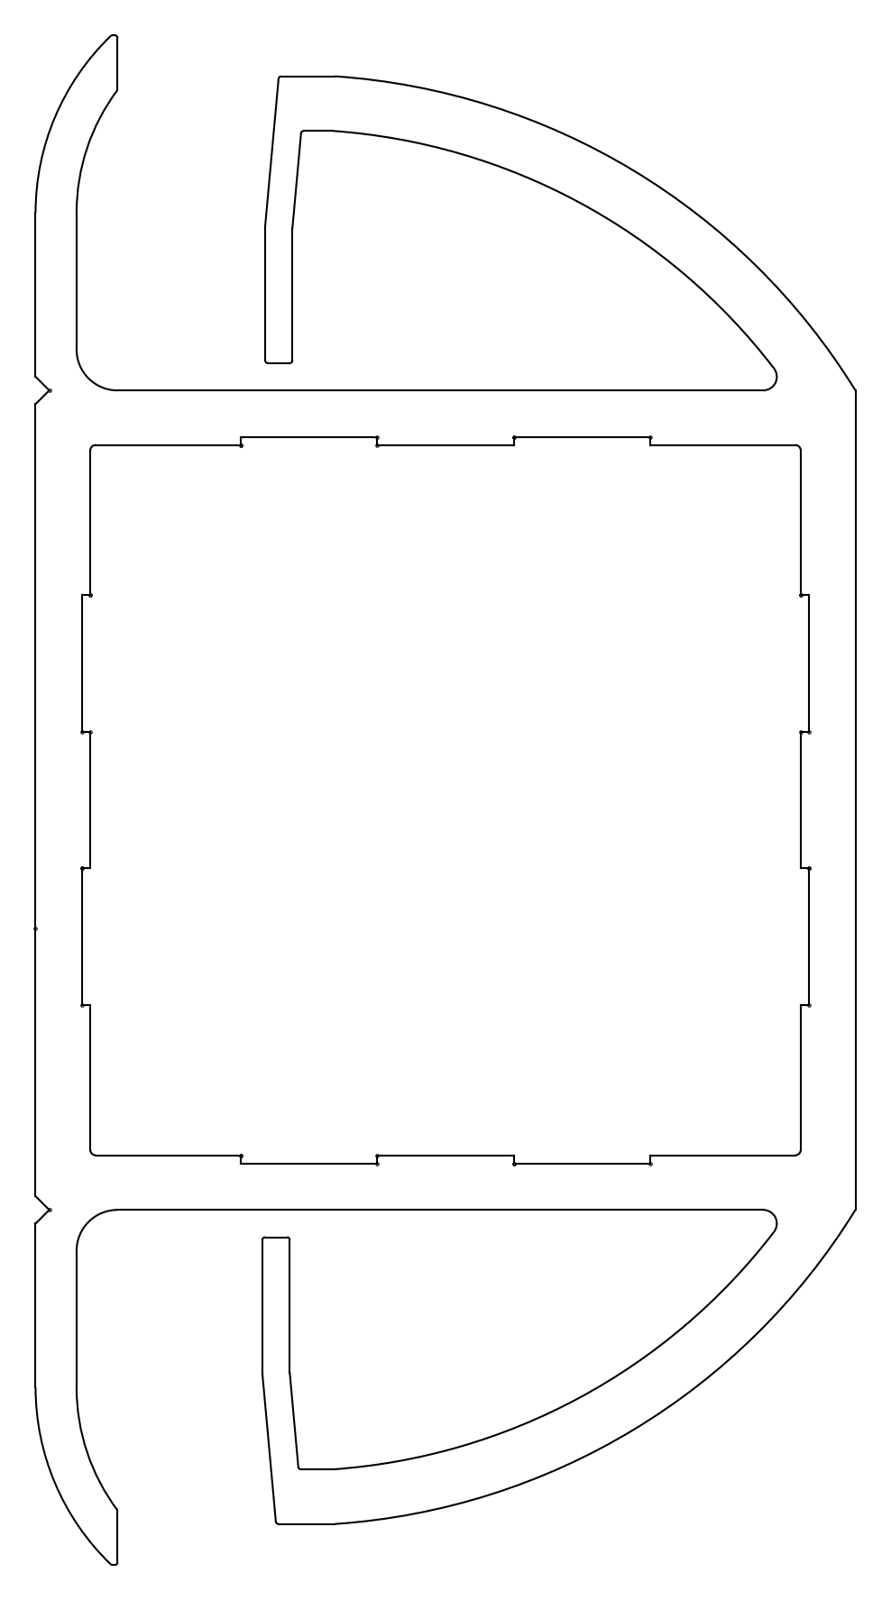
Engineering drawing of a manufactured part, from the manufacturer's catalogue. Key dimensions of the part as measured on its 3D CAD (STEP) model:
STEP written by: THINKDESIGN (CONFIG_CONTROL_DESIGN)
Units: millimetres
Bodies: 1 solid, 96 faces (68 planar, 28 cylindrical, 0 other)
Overall size (bounding box): 100 × 56 × 30
Volume: 36 273 mm³ · Surface area: 41 265 mm²
Partial cylindrical surfaces — rounded edges, fillets, slot ends (radius × count): R0.1 ×12, R0.2 ×4, R0.5 ×2, R1.5 ×2, R7.5 ×2, R9 ×2, R22.31 ×2, R24.31 ×2
Main face-to-face distances: 2, 28, 30, 1.7, 28.3, 26.3, 26, 26.6, 1, 1.5
